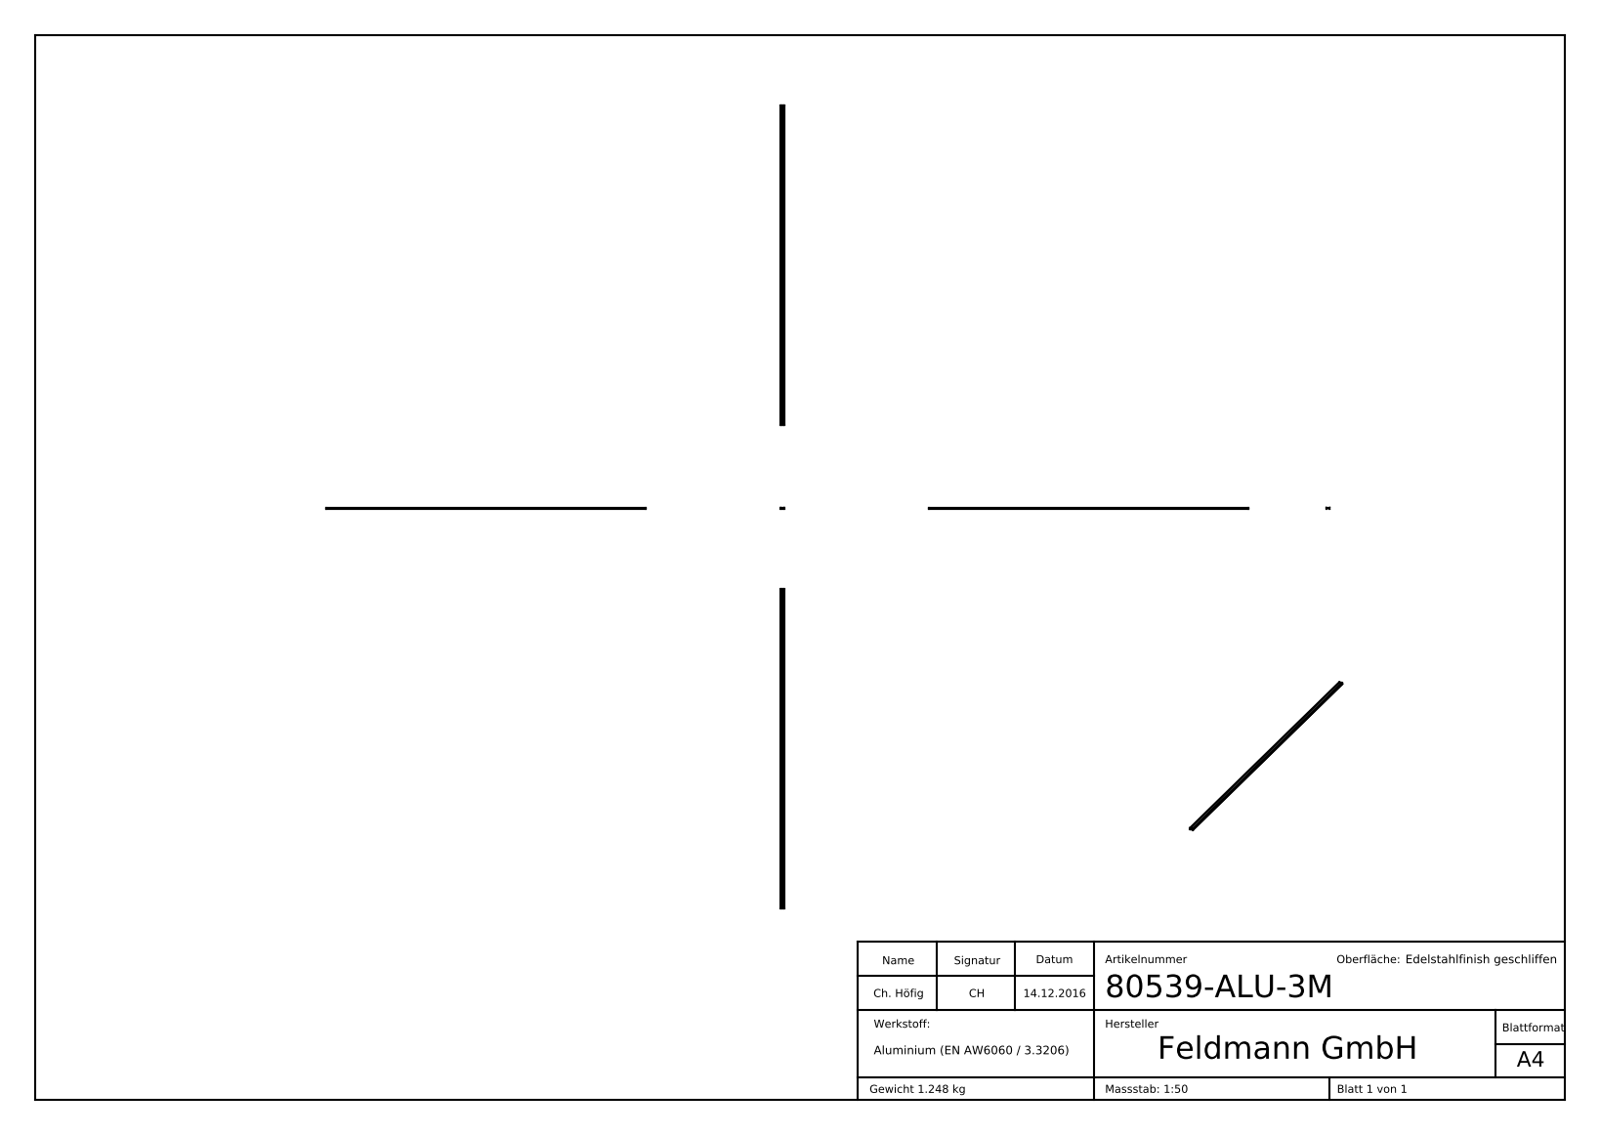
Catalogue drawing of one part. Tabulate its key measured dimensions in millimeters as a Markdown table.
| quantity | value |
| --- | --- |
| part name | 80539-ALU-3M |
| STEP written by | SolidWorks 2015 (CONFIG_CONTROL_DESIGN) |
| units | millimeters |
| bodies | 1 solid, 283 faces (151 planar, 6 cylindrical, 126 other) |
| overall size | 3000 × 30 × 14 |
| volume | 462 205 mm³ |
| surface area | 322 594 mm² |
| partial cylindrical surfaces (radius × count) | 0.5 × 4, 2 × 2 |
| main face-to-face distances | 3, 27, 30, 24, 11, 14, 3000, 2.9, 24.1, 27.1 |
